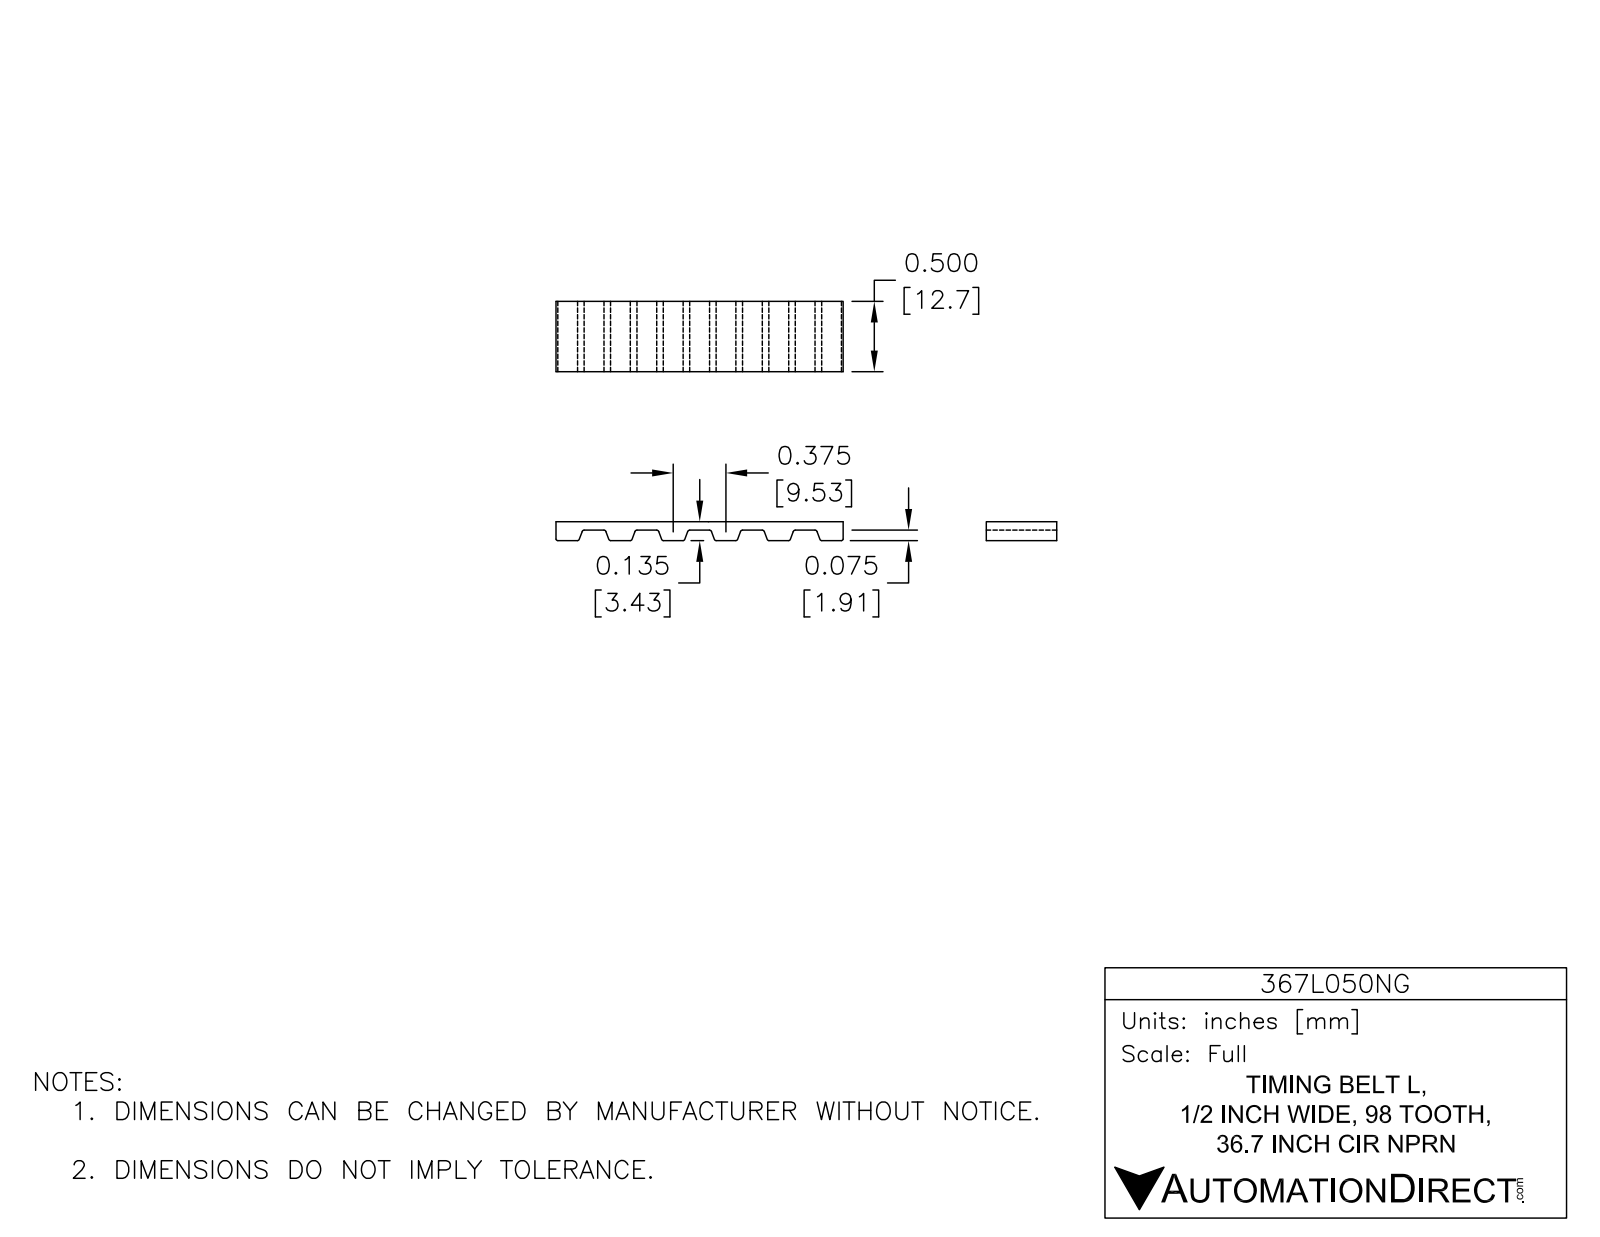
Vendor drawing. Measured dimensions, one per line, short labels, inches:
name: 367L050NG
written by: SolidWorks 2014 (AUTOMOTIVE_DESIGN)
unit: in
bodies: 1 solid, 798 faces (369 planar, 429 cylindrical, 0 other)
size: 16.663 × 3 × 0.5
volume: 1.665 in³; area: 47.6 in²
rounds: 388× R0.02, 2× R1.435, 2× R1.5
face distances: 0.065, 2.935, 3, 2.87, 0.5, 0.14, 2.86, 0.075, 2.795, 2.72
